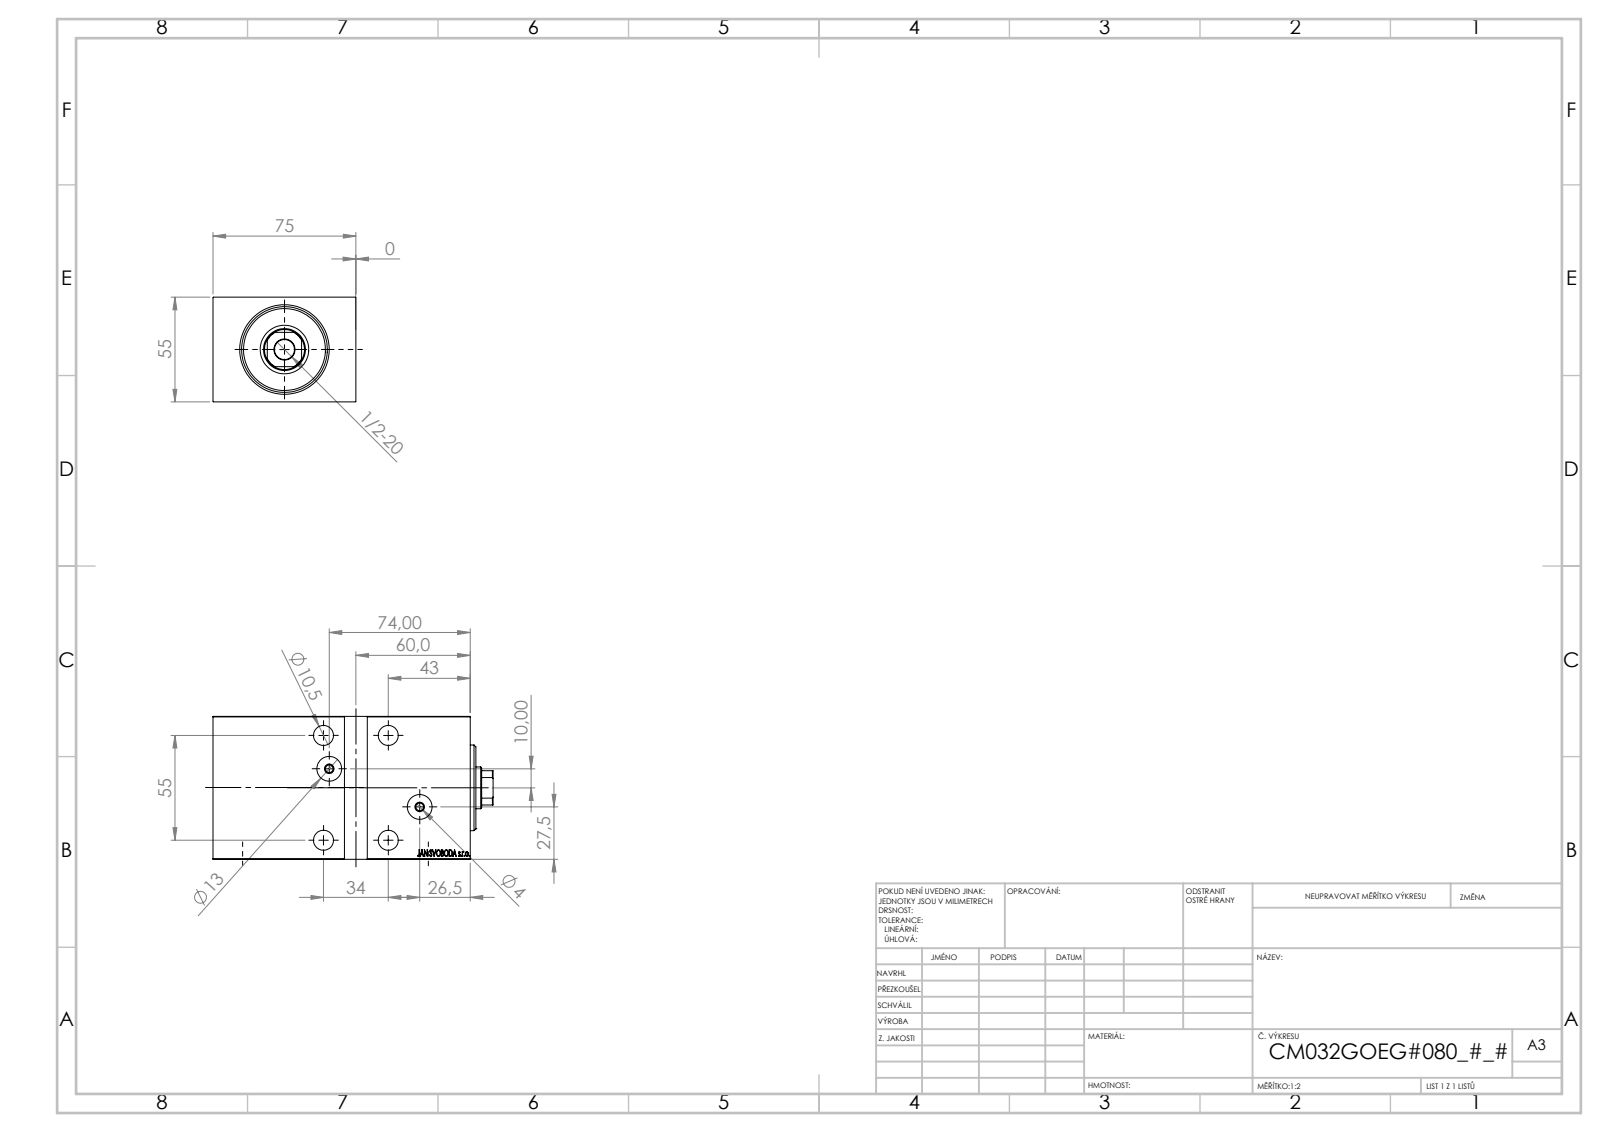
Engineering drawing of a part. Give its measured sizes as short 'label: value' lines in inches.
name: V450CM_VC_G; V450CM_G_Body; Zatka_OIL_PORT; V450CM_G_VCP
written by: SolidWorks 2019 (CONFIG_CONTROL_DESIGN)
unit: in
bodies: 5 solids, 896 faces (442 planar, 56 cylindrical, 398 other)
size: 5.787 × 2.953 × 2.165
volume: 30.43 in³; area: 129.9 in²
holes: 5× ⌀0.413, 4× ⌀0.65, 2× ⌀0.157, 2× ⌀0.512, 1× ⌀0.866, 1× ⌀1.004, 1× ⌀1.26, 1× ⌀1.339, 1× ⌀1.772
bosses: 2× ⌀0.709, 2× ⌀0.197, 1× ⌀1.063
rounds: 1× R0.413
face distances: 2.165, 2.953, 5.315, 0.197, 0.118, 5.118, 4.921, 0.394, 4.724, 5.433
hole spacings: 1.339, 2.165, 2.546, 0.699, 0.947, 1.402, 1.481, 1.613
